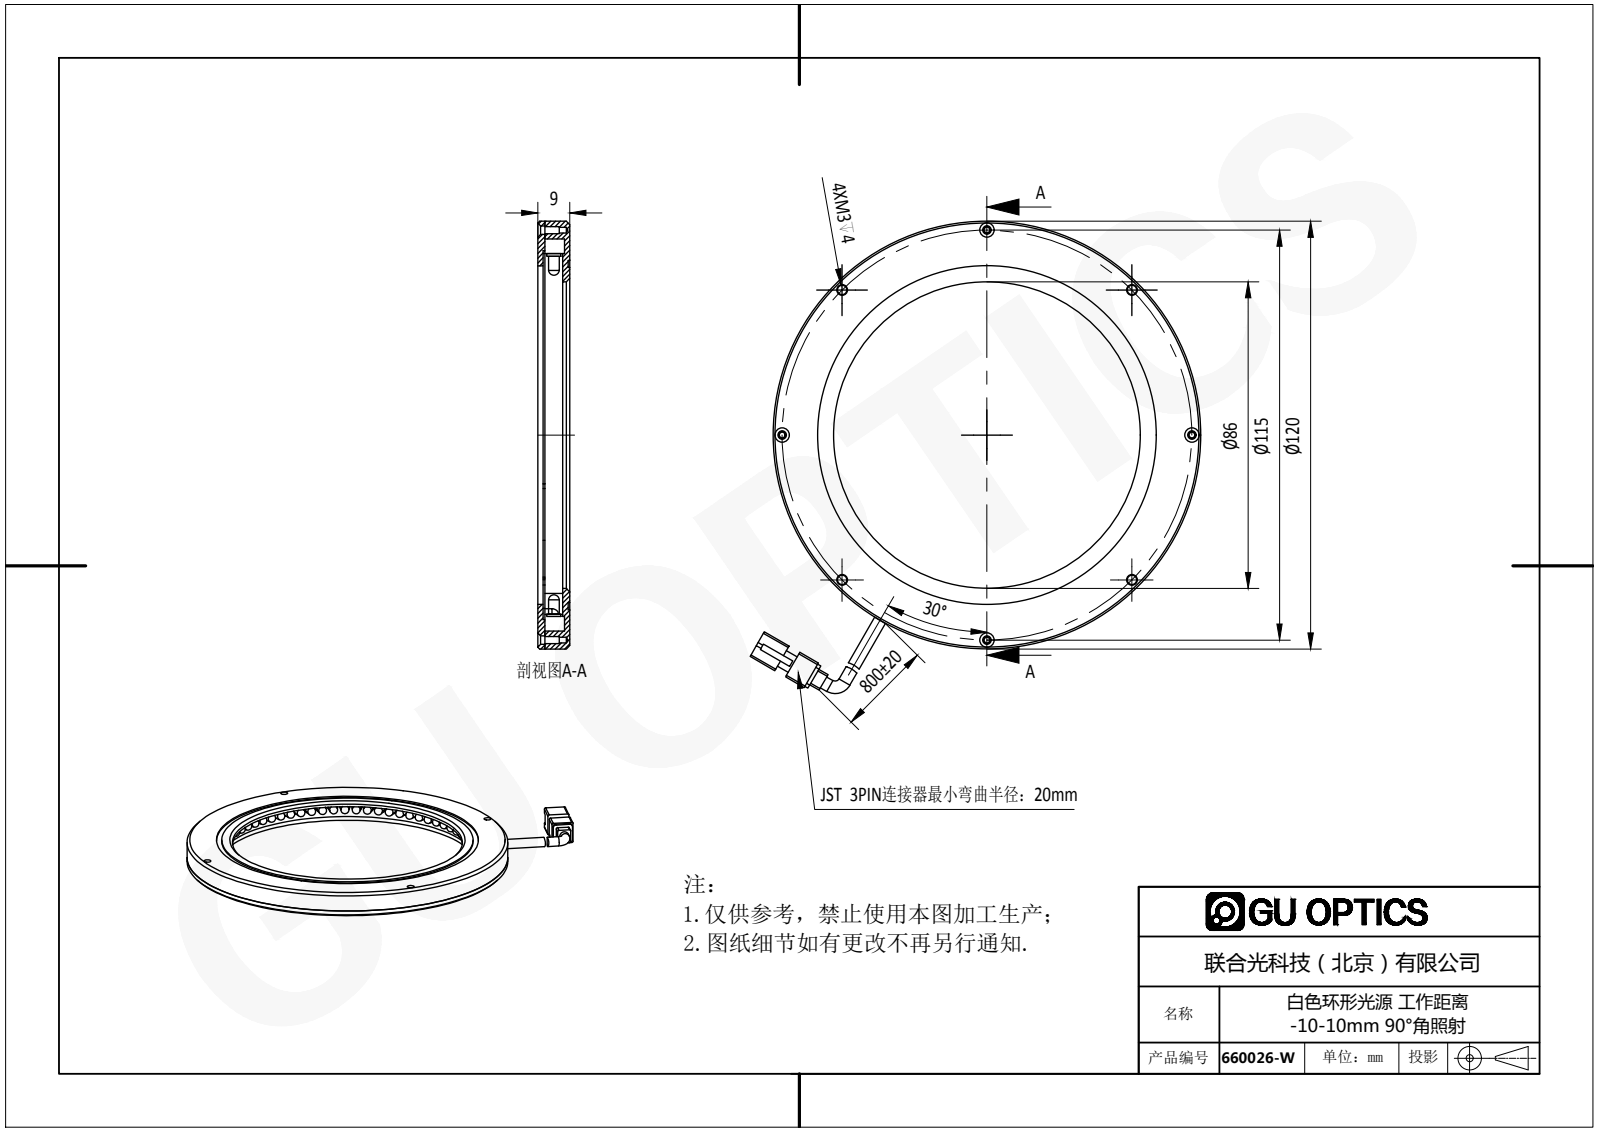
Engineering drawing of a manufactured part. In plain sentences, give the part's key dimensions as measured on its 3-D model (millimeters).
The part is named "660026-W". Its 3-D file was written by "SolidWorks 2016 (AUTOMOTIVE_DESIGN)". It is 75 solids with 1433 faces: 928 planar, 409 cylindrical and 96 other. Overall it measures 132.53 by 126.45 by 11.1 millimeters. Its volume is 30 711 cubic millimeters and its surface area 38 313 square millimeters. Round holes: 4 of diameter 1.6, 4 of diameter 2, 4 of diameter 2.4, 4 of diameter 2.6, 4 of diameter 3, 1 of diameter 3.5, 1 of diameter 86, 1 of diameter 95, 1 of diameter 98, 1 of diameter 103, 1 of diameter 103.5, 1 of diameter 110. Round bosses or shafts: 69 of diameter 3.8, 69 of diameter 3, 2 of diameter 3.5, 1 of diameter 120, 1 of diameter 103.6, 1 of diameter 101.8, 1 of diameter 94. Partial cylindrical surfaces (rounded edges, fillets, slot ends): 12 of radius 1, 8 of radius 0.5, 2 of radius 2.05, 1 of radius 1.8, 1 of radius 7.5, 1 of radius 51.4, 1 of radius 54. The main face-to-face distances are 7, 2, 9, 0.5, 1.5, 5.5, 7.5, 5, 6, 1. The hole center spacings are 44.01, 57.5, 81.32, 106.24, 106.25, 115, 44, 57.49.
